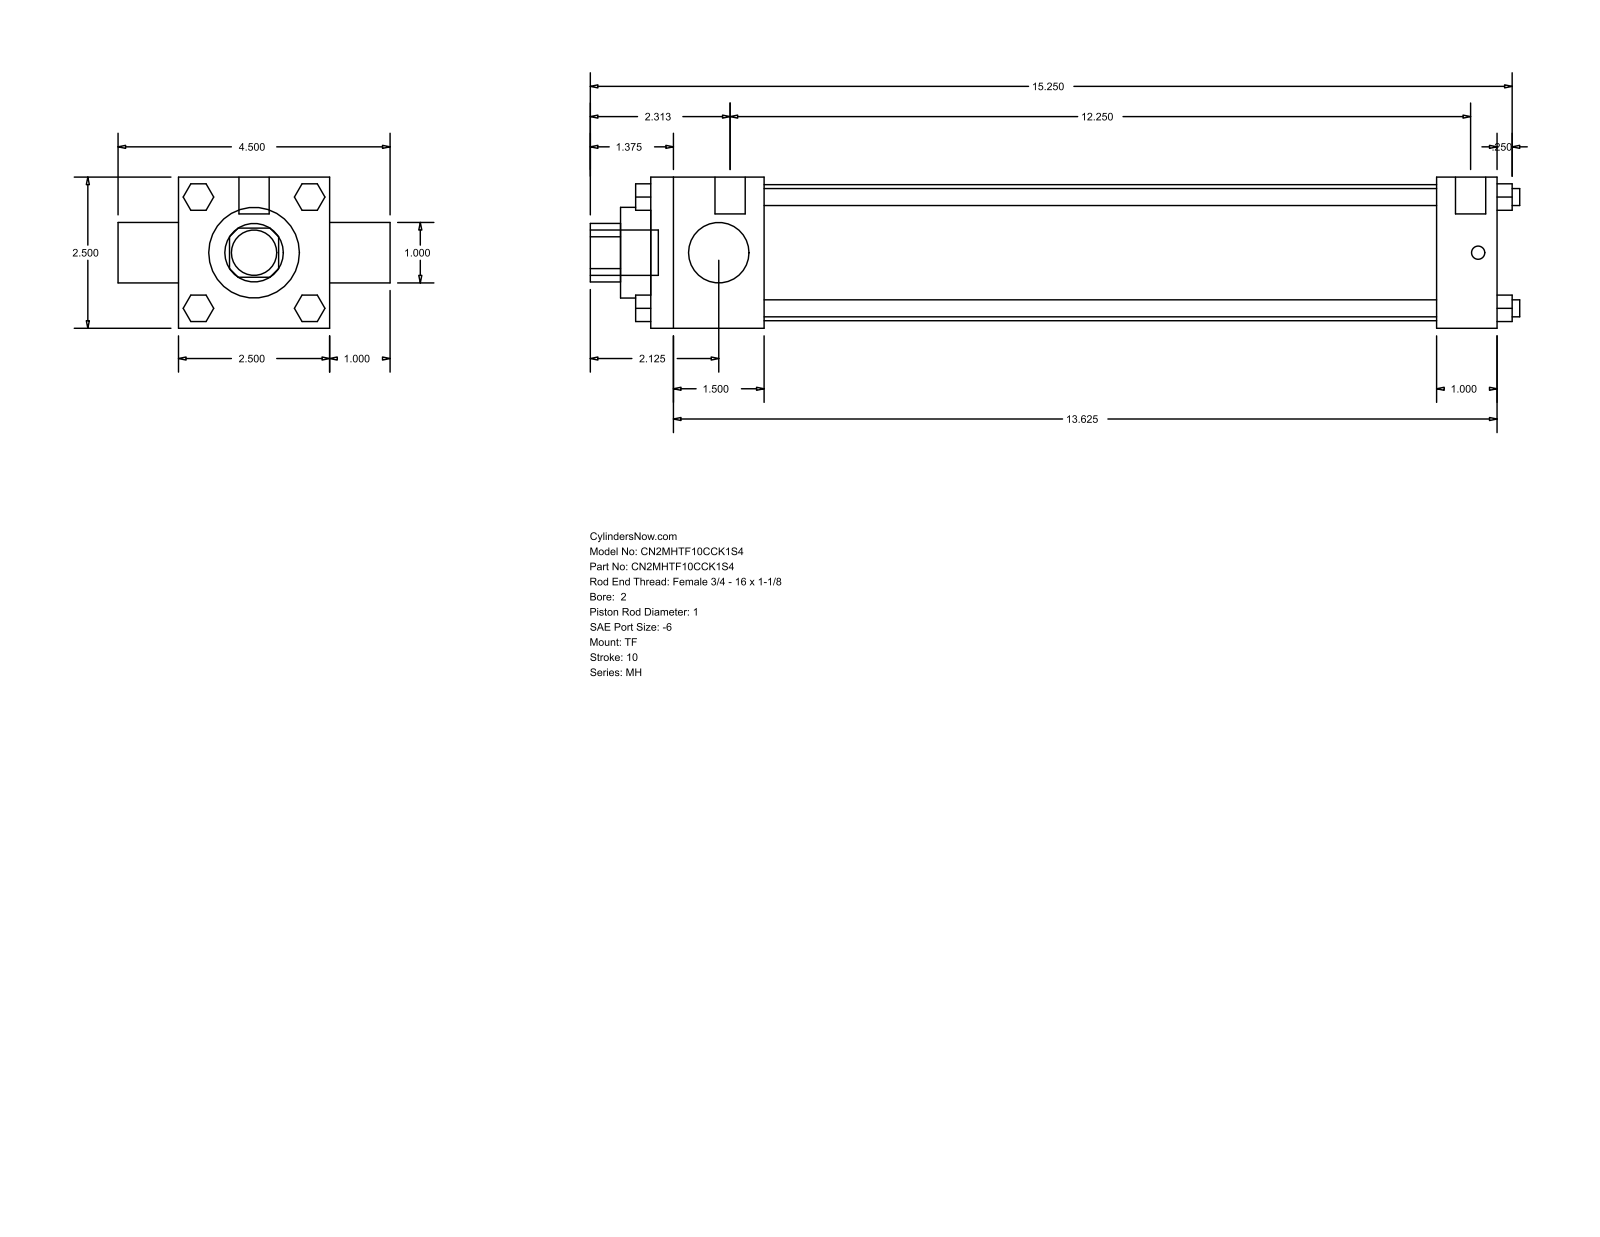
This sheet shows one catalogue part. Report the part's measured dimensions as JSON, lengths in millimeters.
{"part_name": "MH_TF__0200_1", "step_written_by": "GSSL Pune (CONFIG_CONTROL_DESIGN)", "units": "millimeters", "bodies": {"solids": 0, "faces": 120, "planar": 92, "cylindrical": 28, "other": 0}, "overall_size": [390.52, 114.3, 63.5], "round_holes": [[25.4, 2], [38.1, 1], [57.15, 1]], "round_bosses_or_shafts": [[7.14, 4], [5.56, 3], [12.7, 2], [19.05, 1]], "partial_cylinders_radius": [[12.29, 1]], "face_to_face_distances": [63.5, 355.6, 25.4, 47.63, 330.2, 282.57, 307.97, 88.9, 368.3, 6.35]}
